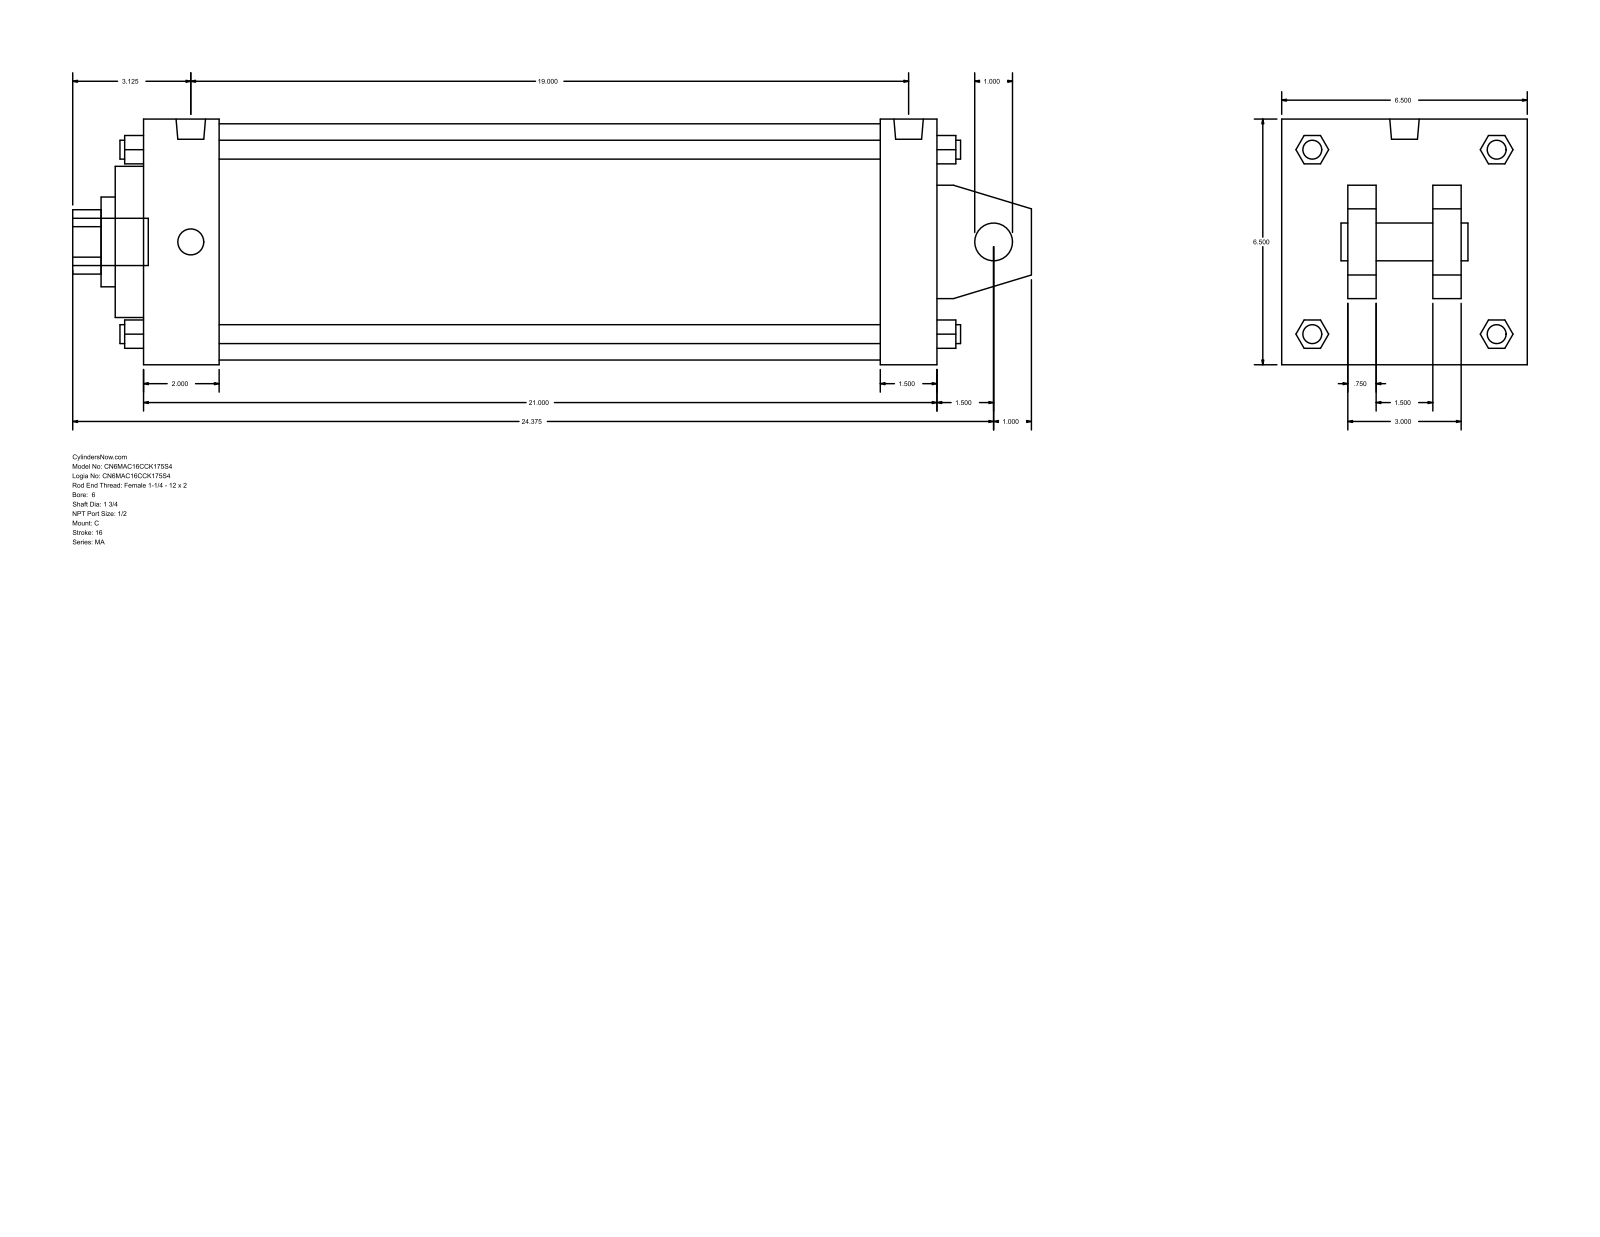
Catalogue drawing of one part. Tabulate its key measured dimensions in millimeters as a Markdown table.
| quantity | value |
| --- | --- |
| part name | MA_C__0600_1.75 |
| STEP written by | GSSL Pune (CONFIG_CONTROL_DESIGN) |
| units | millimeters |
| bodies | 0 solids, 141 faces (109 planar, 32 cylindrical, 0 other) |
| overall size | 644.52 × 165.1 × 165.1 |
| round holes (diameter × count) | 25.4 × 1, 44.45 × 1, 60.33 × 1, 101.6 × 1, 158.75 × 1 |
| round bosses / shafts (diameter × count) | 17.46 × 4, 12.7 × 4, 19.77 × 2, 31.75 × 1 |
| partial cylindrical surfaces (radius × count) | 21.63 × 1 |
| main face-to-face distances | 165.1, 533.4, 19.05, 38.1, 63.5, 101.6, 44.45, 120.65, 57.15, 50.8 |
